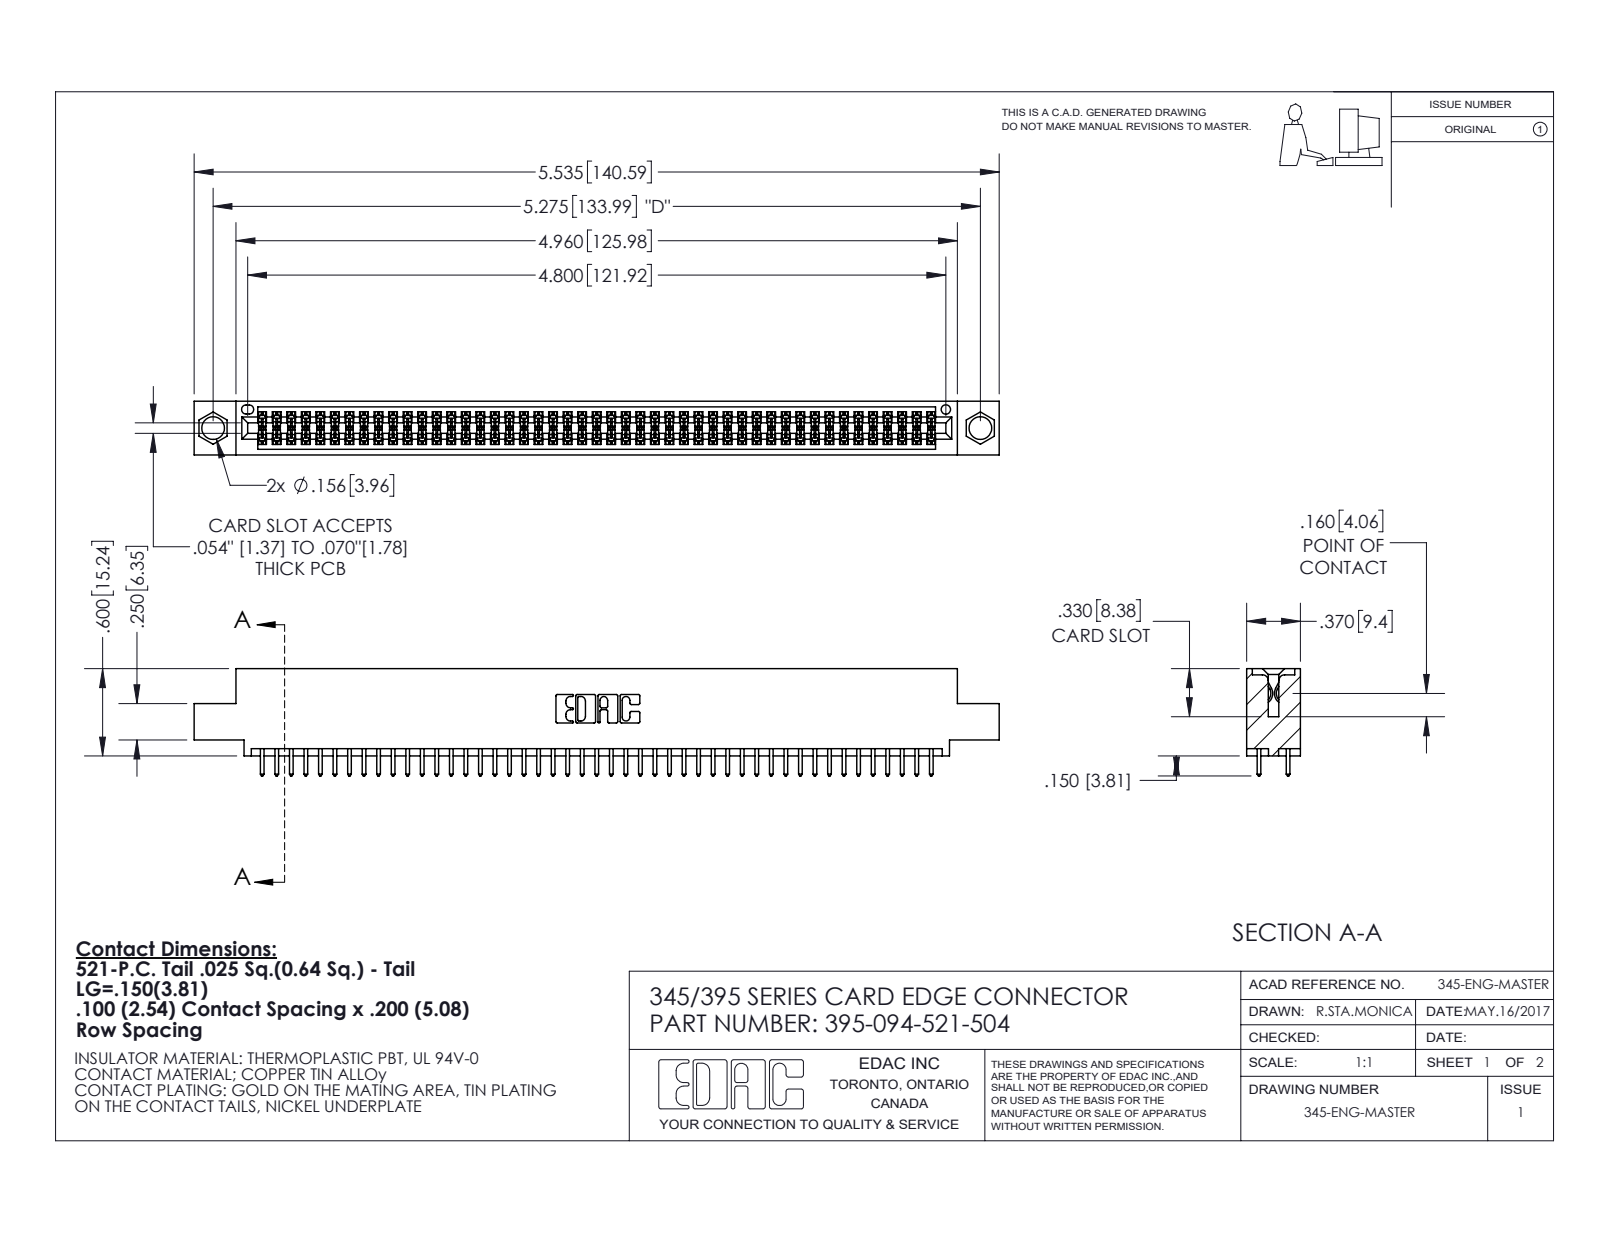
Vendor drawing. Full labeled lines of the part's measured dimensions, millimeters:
Part name (STEP PRODUCT): 395-094-521-504; 345-292-001_345-293-121; 345 Part_0.110 Offset - 0.156 Dia-TI
STEP written by: SolidWorks 2020 (CONFIG_CONTROL_DESIGN)
Units: millimetres
Bodies: 95 solids, 4844 faces (3200 planar, 1644 cylindrical, 0 other)
Overall size (bounding box): 140.6 × 18.7 × 9.4
Volume: 13 500 mm³ · Surface area: 19 720 mm²
Round holes (diameter × count): ⌀4 ×2, ⌀1.6 ×1
Partial cylindrical surfaces — rounded edges, fillets, slot ends (radius × count): R0.2 ×188, R0.3 ×94, R0.3 ×22, R0.2 ×6, R0.8 ×6, R0.7 ×3, R0.4 ×2, R0.5 ×2
Main face-to-face distances: 1.8, 7.6, 5.1, 9.4, 2.5, 6.9, 0.6, 5.7, 4.4, 3.8
Hole centre spacings: 6.9, 128, 134
